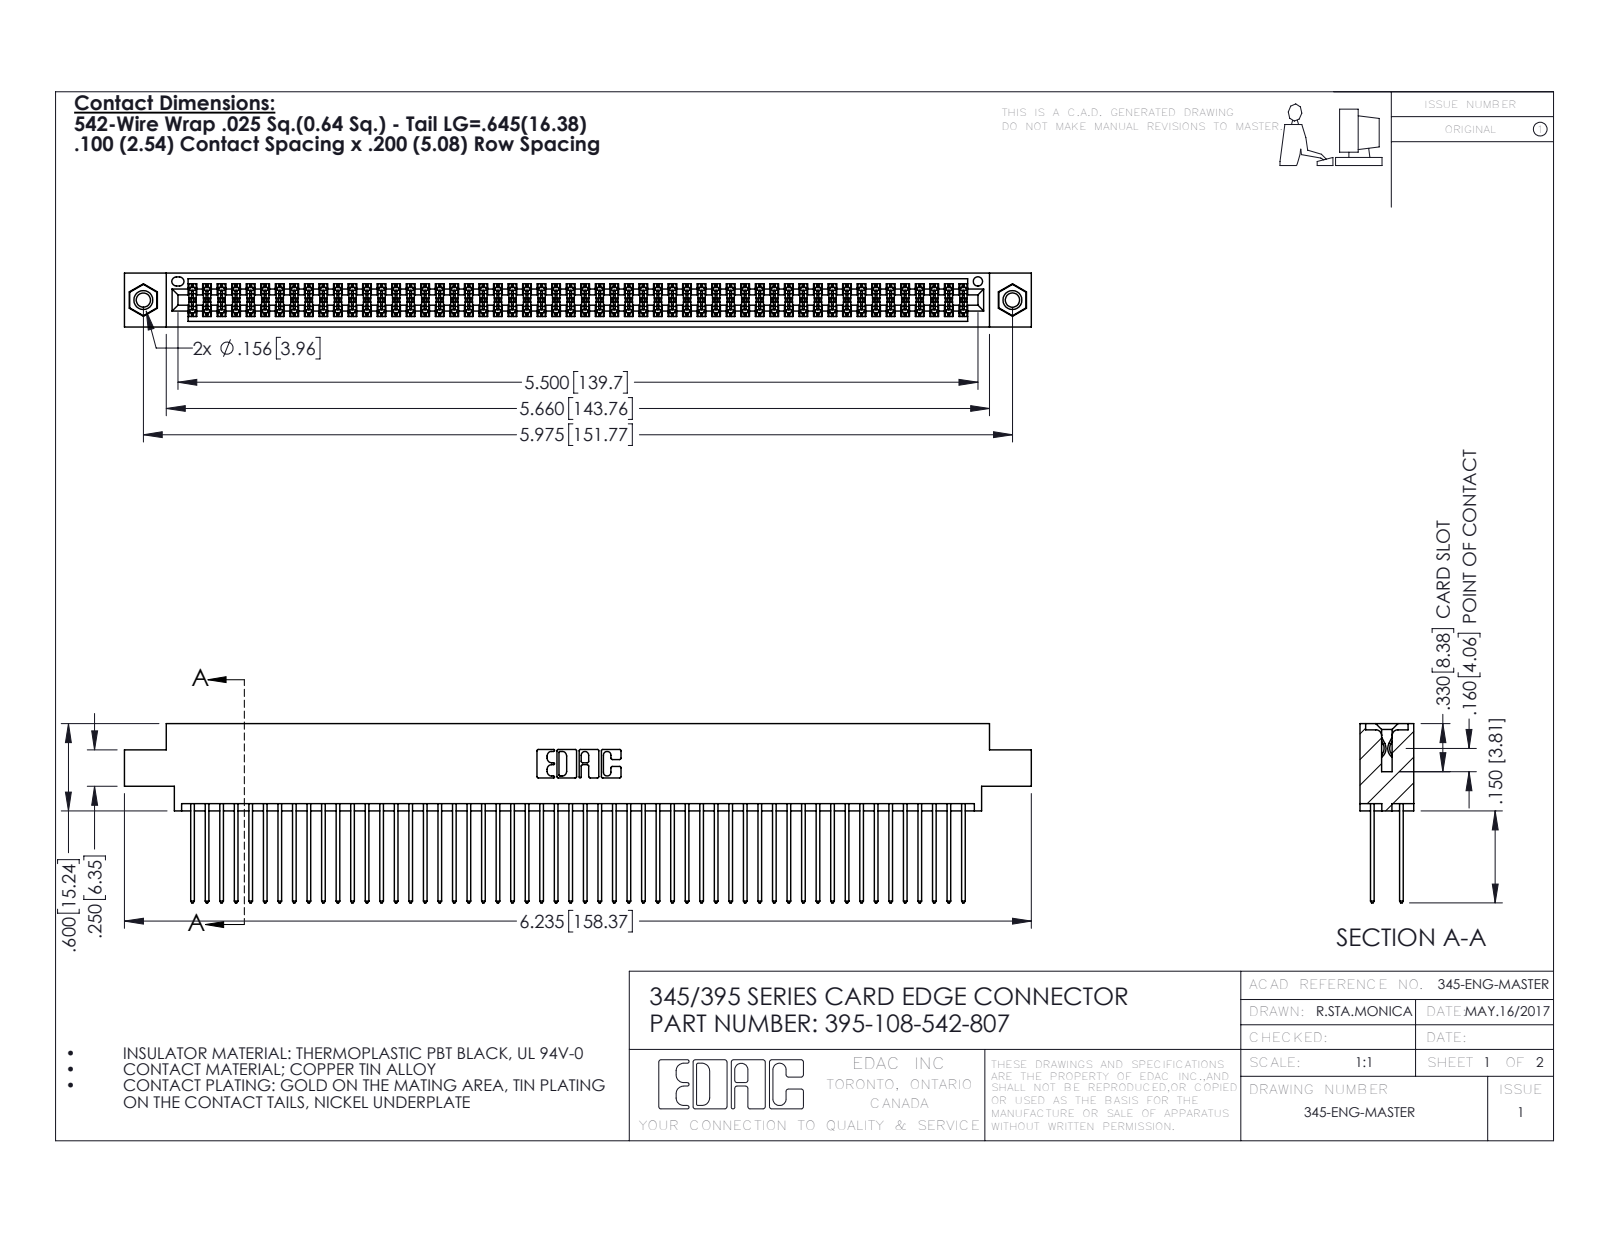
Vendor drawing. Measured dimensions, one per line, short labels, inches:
name: 345-292-001_345-293-142; 395-108-542-807; 345-250-001_345-250-005-103; 345 Part_0.170 Offset - 0.156 Dia-TI
written by: SolidWorks 2016 (CONFIG_CONTROL_DESIGN)
unit: in
bodies: 111 solids, 5590 faces (3680 planar, 1894 cylindrical, 16 other)
size: 6.235 × 1.232 × 0.37
volume: 0.969 in³; area: 40.64 in²
holes: 2× ⌀0.098, 2× ⌀0.125, 2× ⌀0.156, 1× ⌀0.064
bosses: 2× ⌀0.155
rounds: 162× R0.006, 108× R0.01, 22× R0.01, 6× R0.007, 6× R0.031, 3× R0.026, 2× R0.014, 2× R0.019
face distances: 0.072, 0.298, 0.2, 0.098, 0.272, 0.025, 0.37, 0.225, 0.175, 0.149
hole spacings: 0.27, 5.739, 5.975
